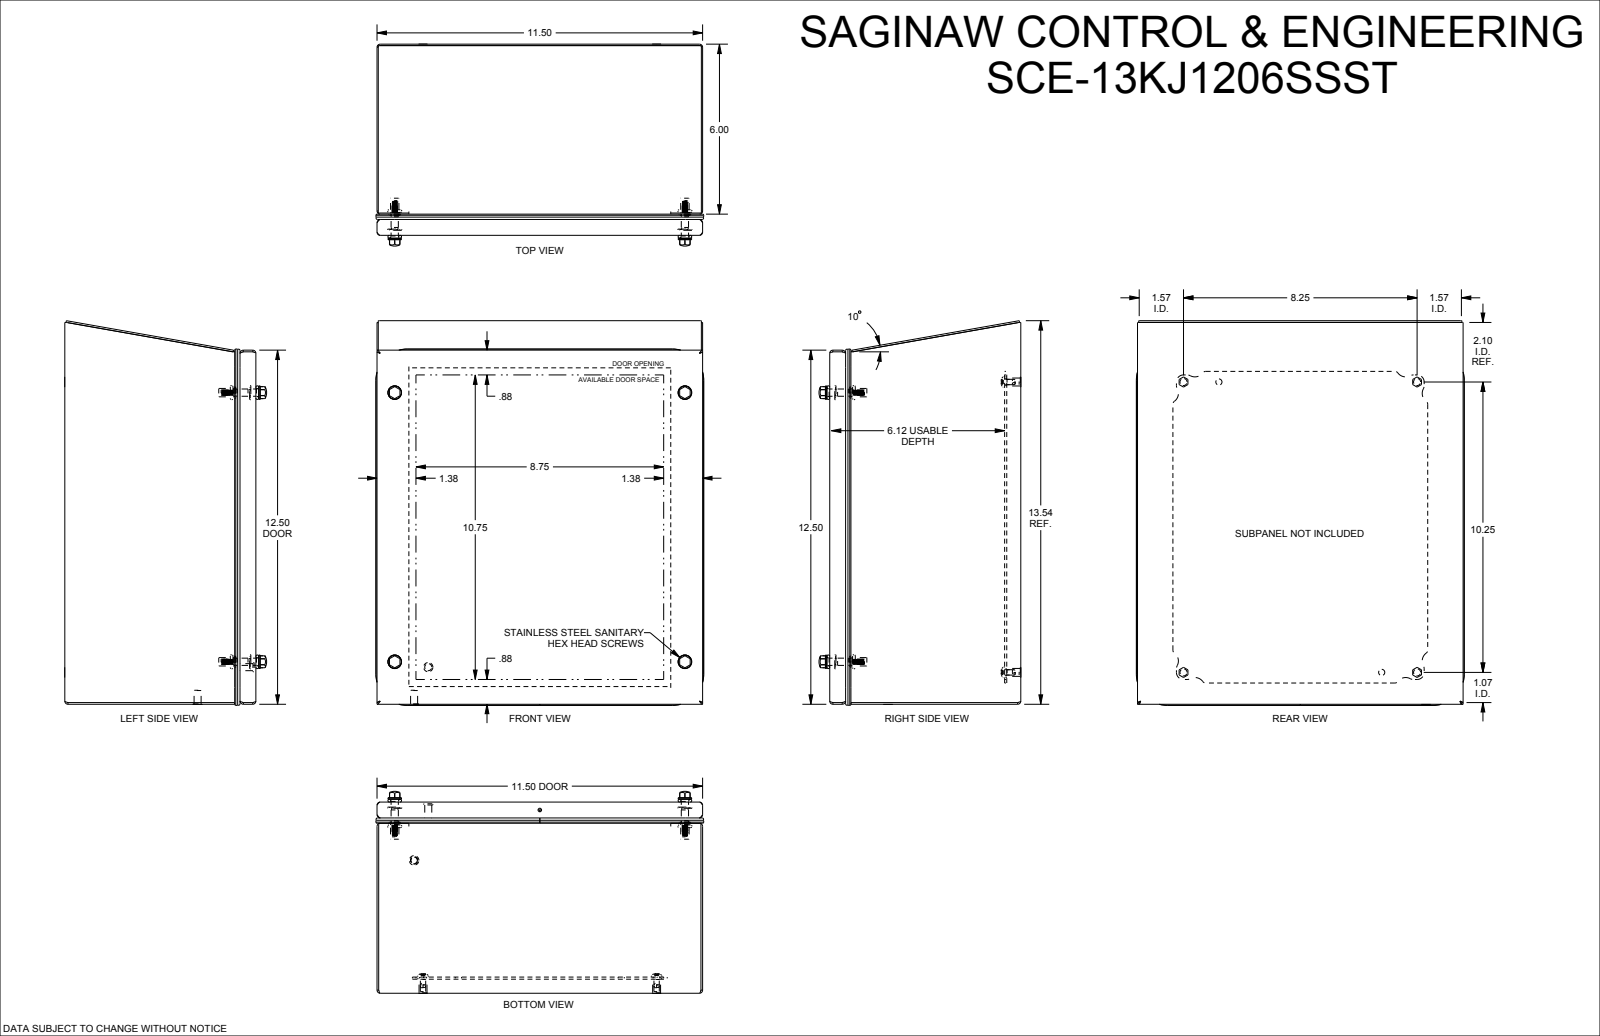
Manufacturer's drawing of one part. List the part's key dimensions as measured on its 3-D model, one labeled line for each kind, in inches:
Part name (STEP PRODUCT): SCE-13KJ1206SSST
STEP written by: SolidWorks 2021 (AUTOMOTIVE_DESIGN)
Units: inches
Bodies: 31 solids, 991 faces (349 planar, 309 cylindrical, 333 other)
Overall size (bounding box): 13.559 × 11.581 × 7.133
Volume: 59.12 in³ · Surface area: 1 766 in²
Round holes (diameter × count): ⌀0.19 ×8, ⌀0.28 ×8, ⌀0.25 ×4, ⌀0.27 ×4, ⌀0.32 ×4, ⌀0.367 ×4, ⌀0.218 ×2
Round bosses / shafts (diameter × count): ⌀0.5 ×4, ⌀0.475 ×4, ⌀0.373 ×4, ⌀0.296 ×4, ⌀0.28 ×4, ⌀0.256 ×4, ⌀0.23 ×4, ⌀0.189 ×4
Partial cylindrical surfaces — rounded edges, fillets, slot ends (radius × count): R0.05 ×26, R0.11 ×26, R0.02 ×20, R0.125 ×12, R0.25 ×12, R0.344 ×8, R0.005 ×4, R0.012 ×4
Main face-to-face distances: 0.06, 6.688, 11.44, 6.628, 6.748, 6.192, 6.252, 0.571, 0.511, 6.117
Hole centre spacings: 9.5, 9.925, 10.245, 8.25, 9.252, 9.253, 9.926, 10.25
